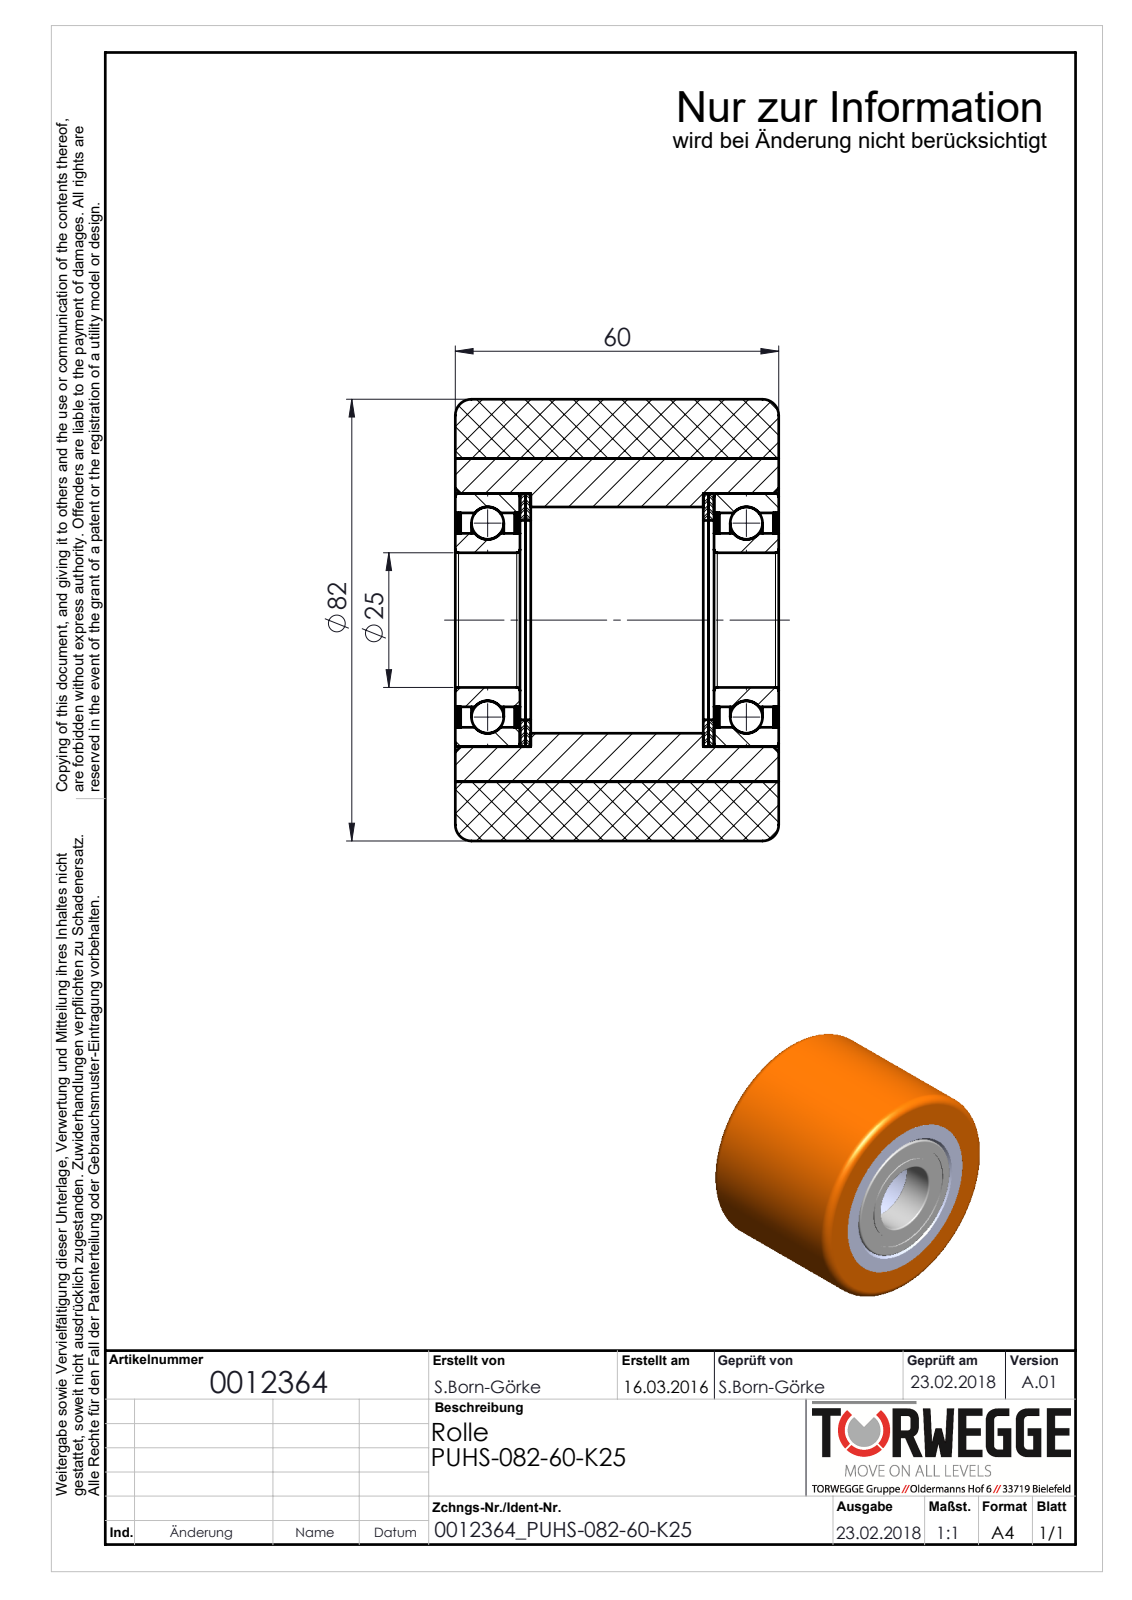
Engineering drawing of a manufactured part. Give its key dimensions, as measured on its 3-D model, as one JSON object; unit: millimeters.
{"part_name": "0012364_PUHS-082-60-K25", "step_written_by": "SolidWorks 2016 (AUTOMOTIVE_DESIGN)", "units": "millimeters", "bodies": {"solids": 16, "faces": 158, "planar": 30, "cylindrical": 68, "other": 60}, "overall_size": [82, 82, 60], "volume_mm3": 250308, "surface_area_mm2": 81952, "round_holes": [[25, 1], [32.2, 1], [37, 1], [39.8, 1], [42, 1], [60, 1]], "round_bosses_or_shafts": [[82, 1], [47, 1]], "face_to_face_distances": [1, 48, 12, 0.5, 13, 47, 35, 60, 34, 46]}
